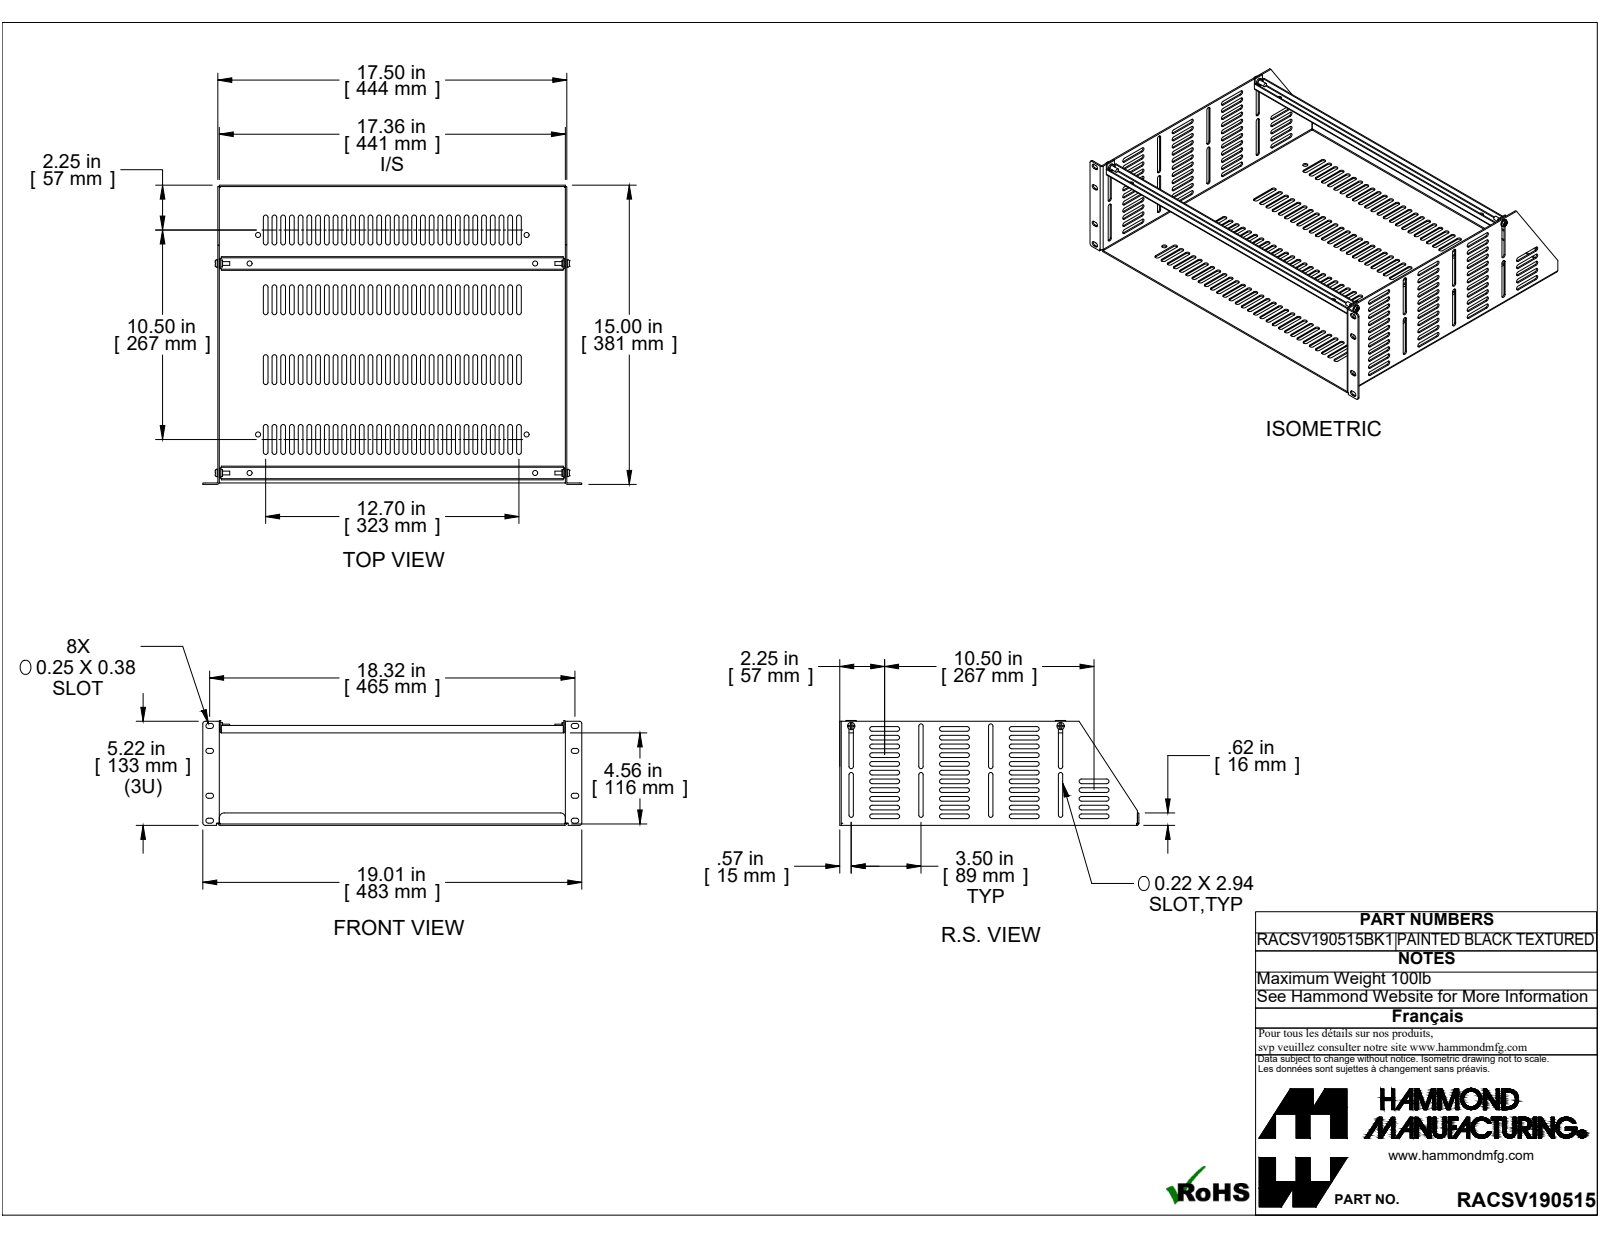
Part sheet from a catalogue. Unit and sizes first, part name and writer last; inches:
Units: inches
Overall size (bounding box): 19.006 × 15 × 5.258
Round holes (diameter × count): ⌀0.25 ×6, ⌀0.159 ×2
Round bosses / shafts (diameter × count): ⌀0.368 ×2, ⌀0.34 ×2, ⌀0.244 ×2, ⌀0.189 ×2
Partial cylindrical surfaces — rounded edges, fillets, slot ends (radius × count): R0.118 ×302, R0.125 ×20, R0.109 ×16, R0.117 ×14, R0.029 ×6, R0.086 ×6, R0.036 ×5, R0.108 ×5
Main face-to-face distances: 0.072, 17.428, 17.5, 17.356, 0.057, 10.5, 0.631, 4.635, 4.692, 4.563
Hole centre spacings: 10, 13.468, 16.774, 10.5
Volume: 27.32 in³ · Surface area: 841.5 in²
Bodies: 11 solids, 1130 faces (606 planar, 508 cylindrical, 16 other)
Part name (STEP PRODUCT): RACSV190515
STEP written by: SolidWorks 2019 (CONFIG_CONTROL_DESIGN)
